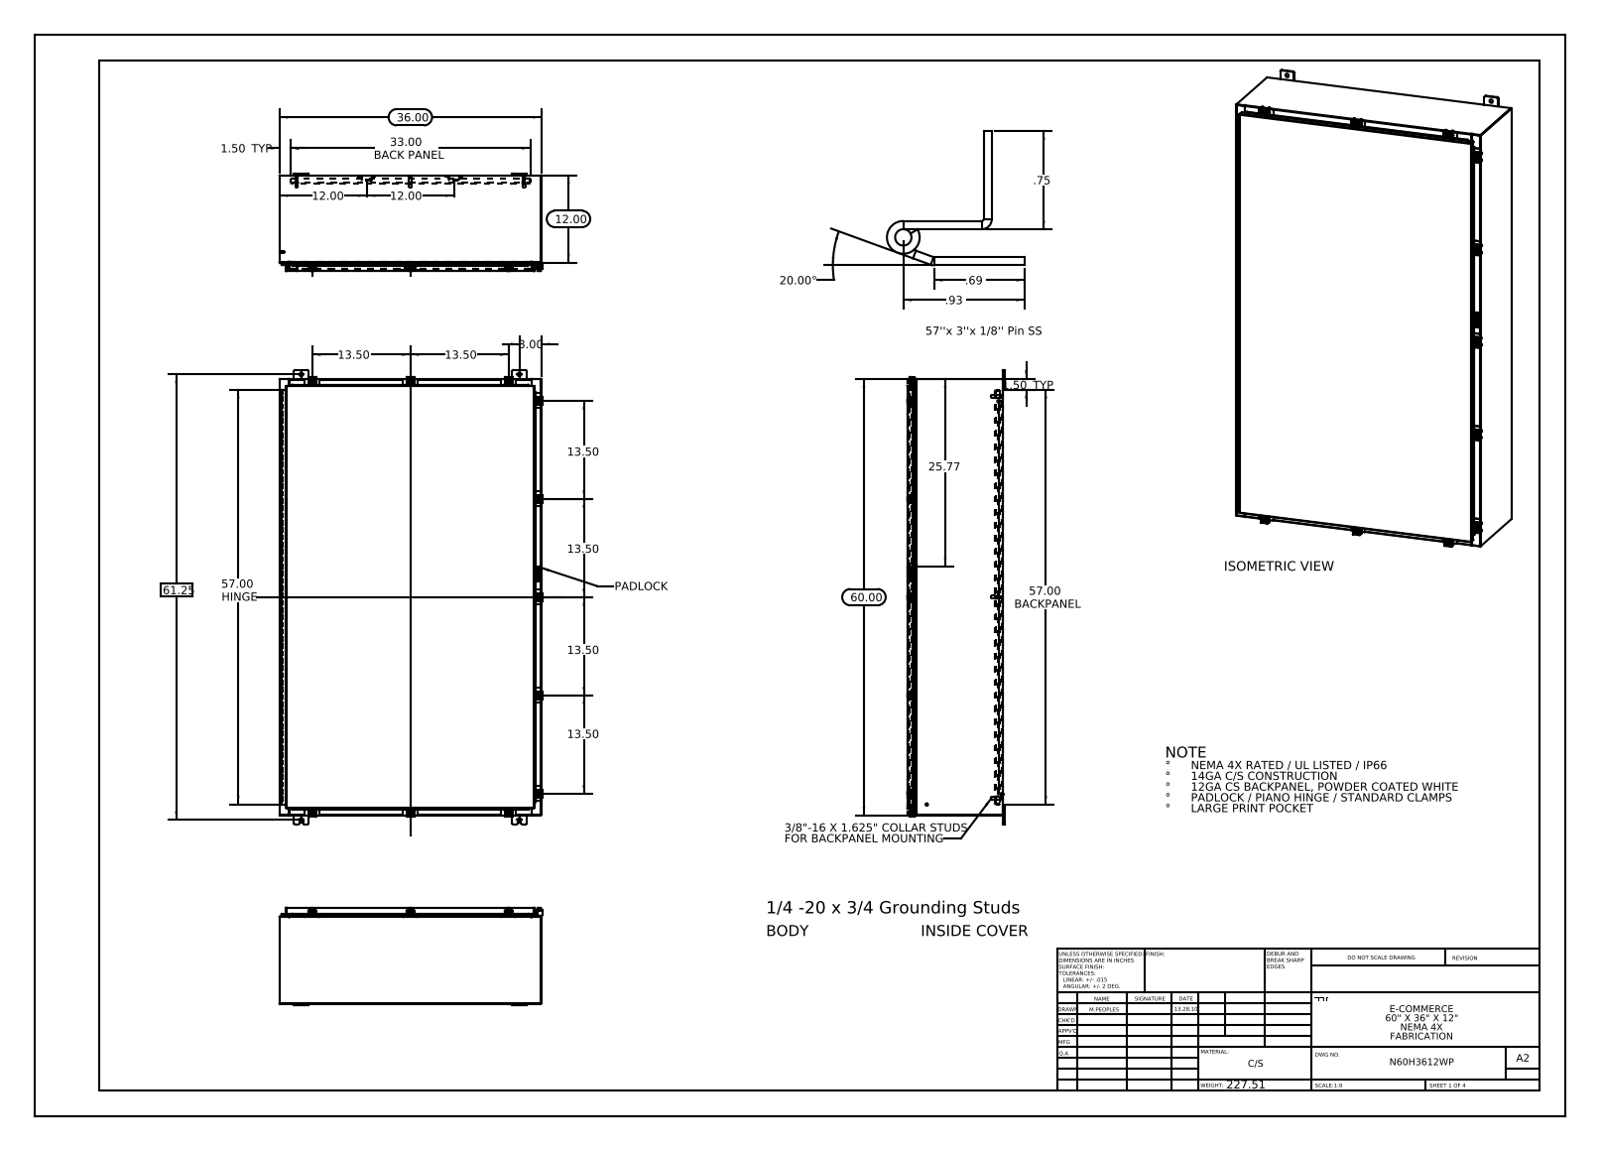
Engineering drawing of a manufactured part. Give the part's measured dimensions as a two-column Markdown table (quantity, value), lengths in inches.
| quantity | value |
| --- | --- |
| part name | N60H3612SSWP Clamp Top; N60H3612SSWP Mounting Studs; N60H3612SSWP 22104005_DEFAULT; N60H3612SSWP Backpanel (+8 more) |
| STEP written by | SolidWorks 2013 (CONFIG_CONTROL_DESIGN) |
| units | inches |
| bodies | 89 solids, 3554 faces (1796 planar, 1506 cylindrical, 252 other) |
| overall size | 62.5 × 36.211 × 13.389 |
| volume | 796.1 in³ |
| surface area | 19 854 in² |
| round holes (diameter × count) | 0.5 × 12, 0.213 × 11, 0.26 × 11, 0.25 × 8, 0.125 × 2 |
| round bosses / shafts (diameter × count) | 0.25 × 12, 0.5 × 11, 0.399 × 11, 0.625 × 8, 0.375 × 8, 0.33 × 8, 0.157 × 8, 0.14 × 8 |
| partial cylindrical surfaces (radius × count) | 0.06 × 50, 0.013 × 39, 0.088 × 33, 0.19 × 24, 0.12 × 22, 0.141 × 22, 0.05 × 17, 0.08 × 16 |
| main face-to-face distances | 0.075, 13.126, 13.051, 0.104, 13.201, 1, 12.126, 1.075, 12.051, 1.179 |
| hole center spacings | 13.5, 13.663, 2.225, 27, 27.625, 29.802, 41.709, 57.39 |
